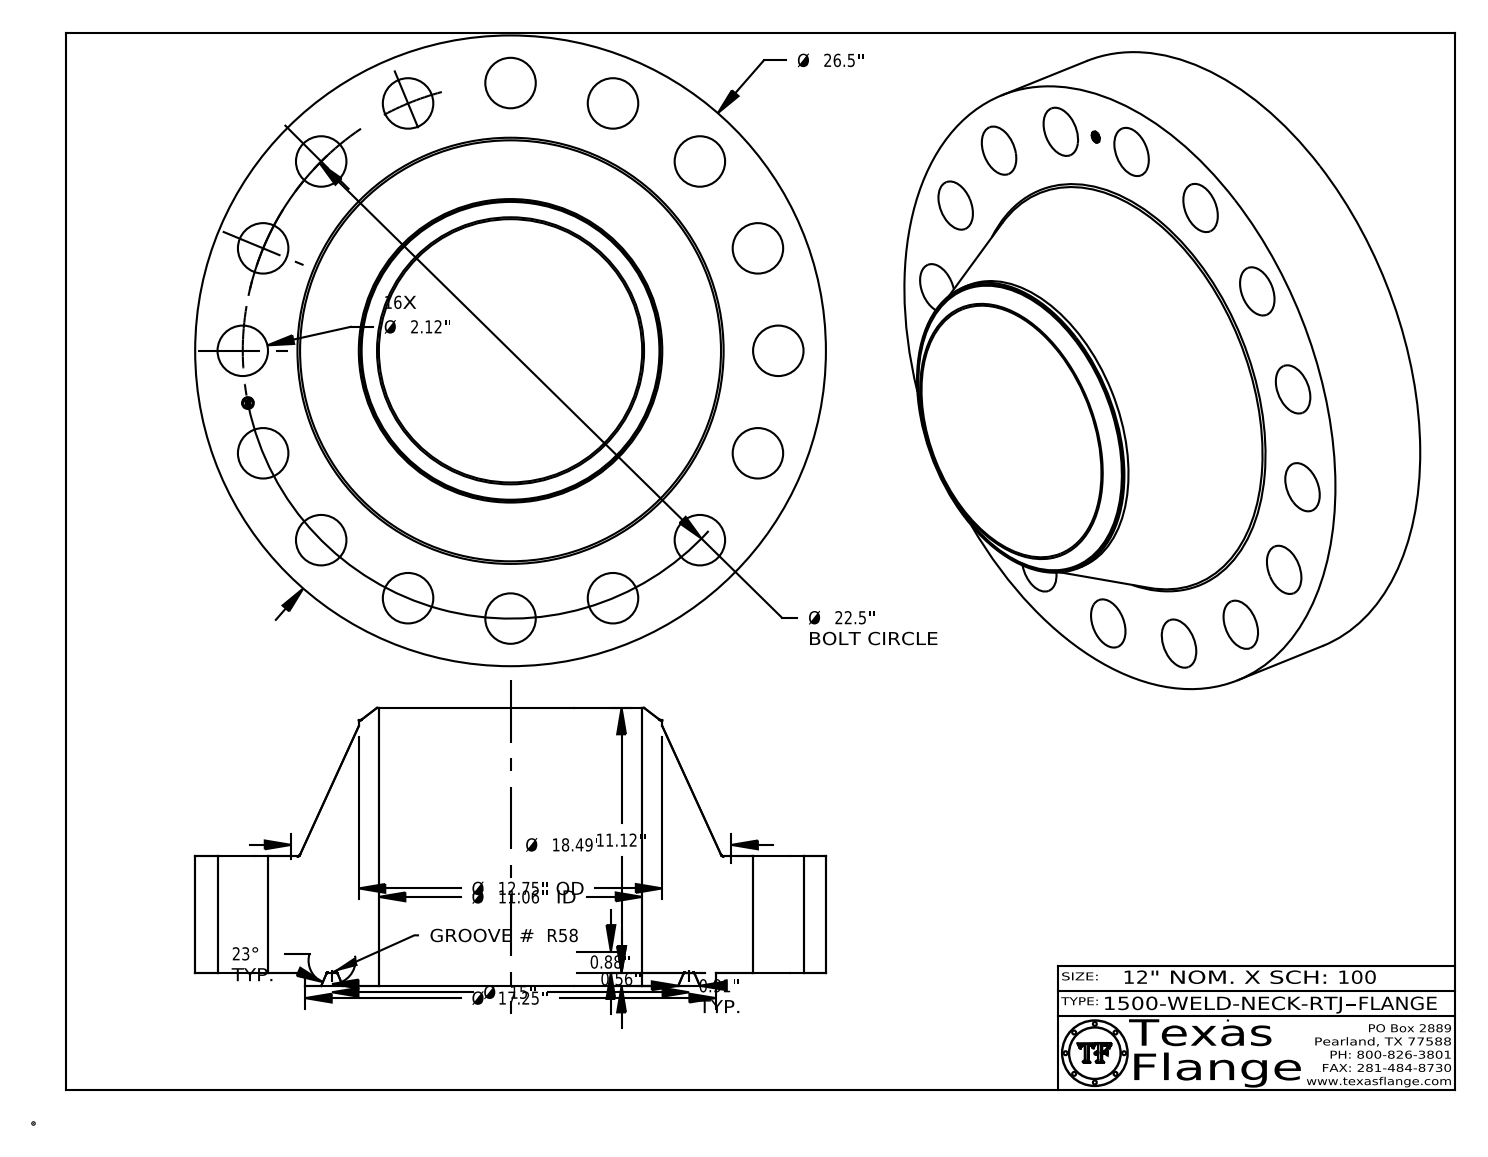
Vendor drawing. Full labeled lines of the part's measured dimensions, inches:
Part name (STEP PRODUCT): 1500-WELD-NECK-RTJ
STEP written by: CATIA V5 STEP AP214 (AUTOMOTIVE_DESIGN)
Units: inches
Bodies: 1 solid, 449 faces (371 planar, 60 cylindrical, 18 other)
Overall size (bounding box): 26.5 × 26.5 × 11.683
Volume: 2 505 in³ · Surface area: 2 379 in²
Round holes (diameter × count): ⌀2.12 ×16, ⌀0.495 ×1, ⌀11.062 ×1
Round bosses / shafts (diameter × count): ⌀0.03 ×8, ⌀26.5 ×1, ⌀17.25 ×1, ⌀12.75 ×1, ⌀0.39 ×1
Main face-to-face distances: 4.88, 0.563, 5.443, 11.683, 11.12, 6.24, 5.428, 4.865, 0.015, 6.255
Hole centre spacings: 12.5, 20.787, 22.068, 11.25, 8.611, 15.91, 4.389, 4.39
